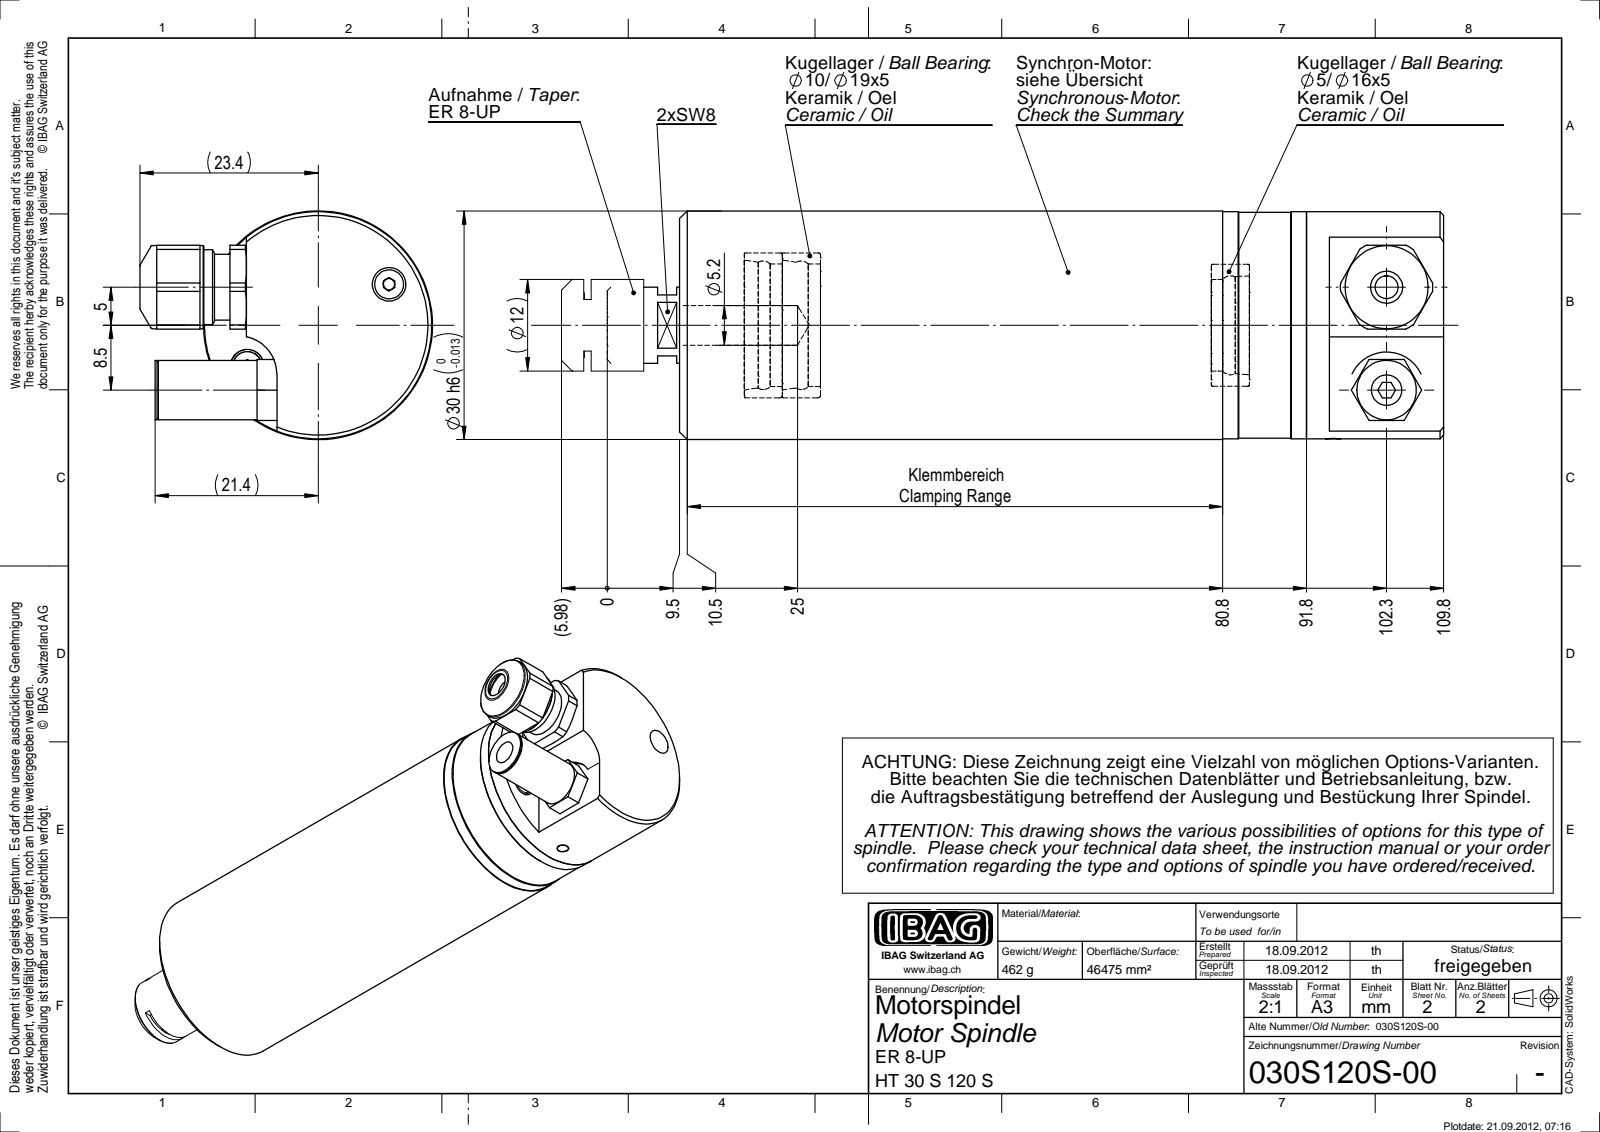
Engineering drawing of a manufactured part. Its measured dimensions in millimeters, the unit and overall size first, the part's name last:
Units: millimetres
Overall size (bounding box): 115.78 × 38.4 × 30
Round holes (diameter × count): ⌀3 ×2, ⌀4.4 ×2, ⌀4 ×1, ⌀4.2 ×1, ⌀5.2 ×1, ⌀9.15 ×1, ⌀10.6 ×1
Round bosses / shafts (diameter × count): ⌀30 ×1, ⌀29.8 ×1, ⌀29.6 ×1, ⌀22.6 ×1, ⌀12 ×1, ⌀10.9 ×1, ⌀10 ×1, ⌀9.79 ×1
Partial cylindrical surfaces — rounded edges, fillets, slot ends (radius × count): R5 ×2, R4.25 ×1, R6.05 ×1
Main face-to-face distances: 100.3, 11, 71.3, 29, 1.8, 69.5, 98.5, 18, 82.3, 80.5
Hole centre spacings: 10.75, 13.5, 21.51
Bodies: 0 solids, 181 faces (81 planar, 67 cylindrical, 33 other)
Part name (STEP PRODUCT): 030S120S-00
STEP written by: SolidWorks 2012 (CONFIG_CONTROL_DESIGN)
